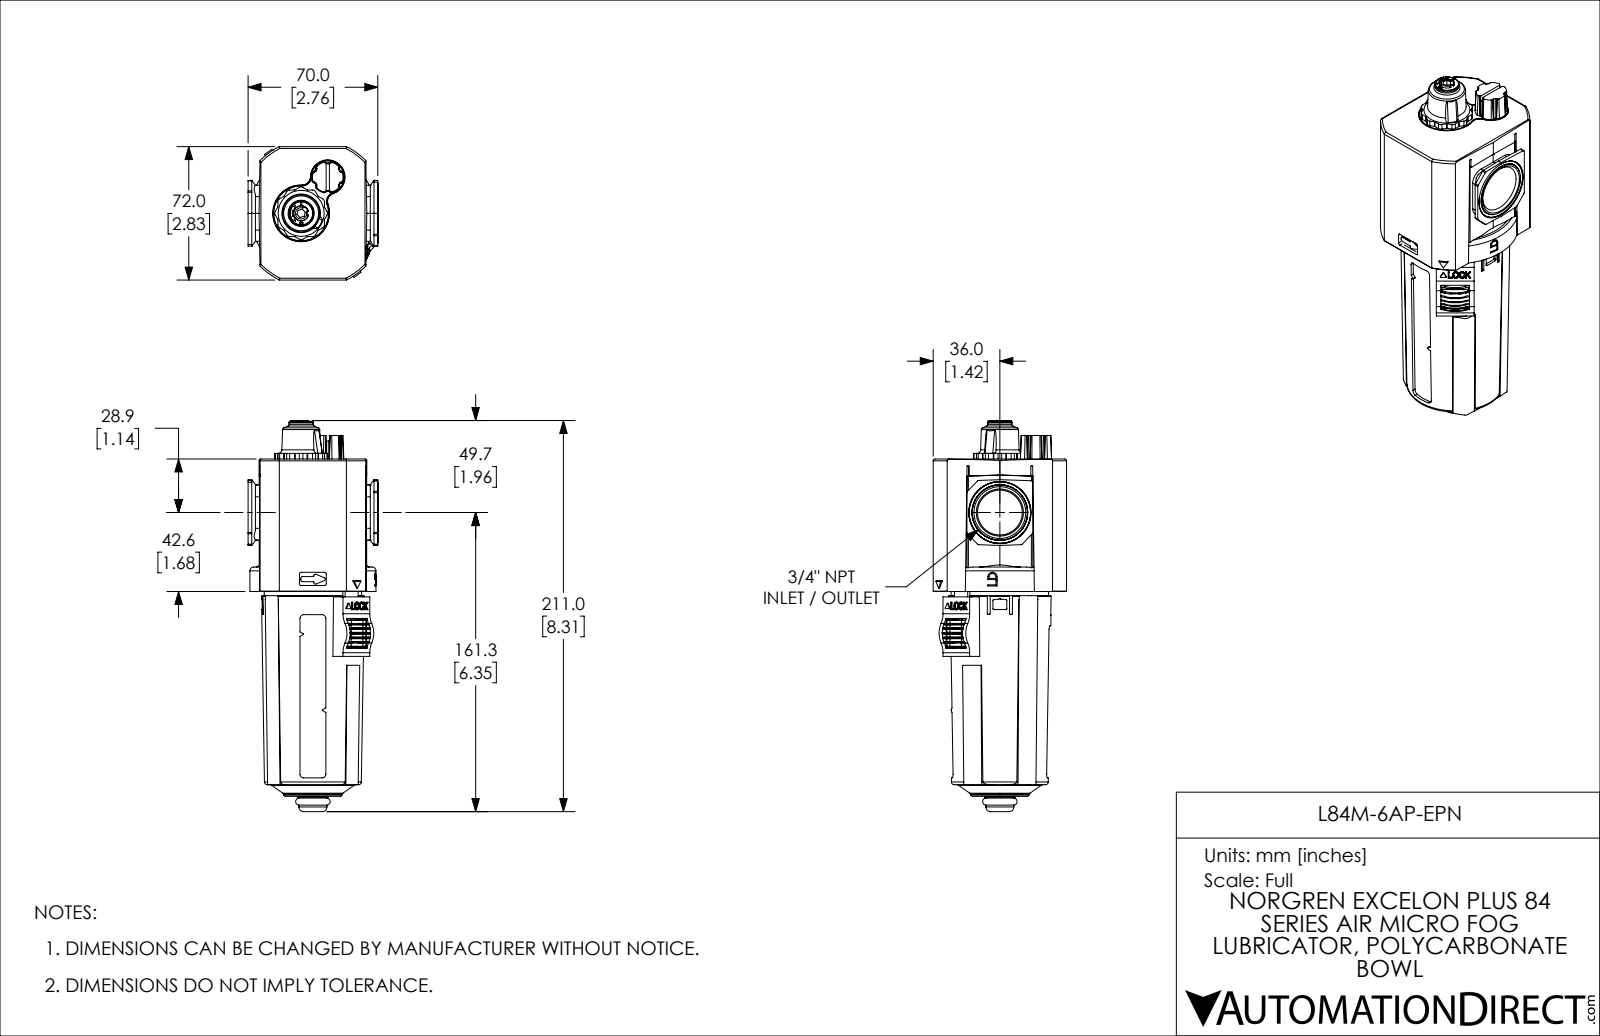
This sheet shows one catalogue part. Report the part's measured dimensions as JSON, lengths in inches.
{"part_name": "L84M-6AP-EPN", "step_written_by": "SolidWorks 2021 (CONFIG_CONTROL_DESIGN)", "units": "inches", "bodies": {"solids": 7, "faces": 1246, "planar": 539, "cylindrical": 422, "other": 285}, "overall_size": [8.306, 2.835, 2.766], "volume_in3": 28.78, "surface_area_in2": 155.6, "round_holes": [[0.126, 1], [0.268, 1], [0.315, 1], [0.969, 1], [2.461, 1]], "round_bosses_or_shafts": [[1.161, 1], [0.99, 1], [0.917, 1], [0.906, 1], [0.856, 1], [0.626, 1], [0.594, 1], [0.51, 1]], "partial_cylinders_radius": [[0.01, 24], [0.02, 21], [0.039, 20], [0.004, 18], [0.028, 16], [0.03, 16], [0.025, 12], [0.075, 12]], "face_to_face_distances": [2.411, 0.059, 2.352, 2.835, 0.035, 2.317, 2.376, 2.756, 0.404, 0.439], "hole_center_spacings": [0.25]}
